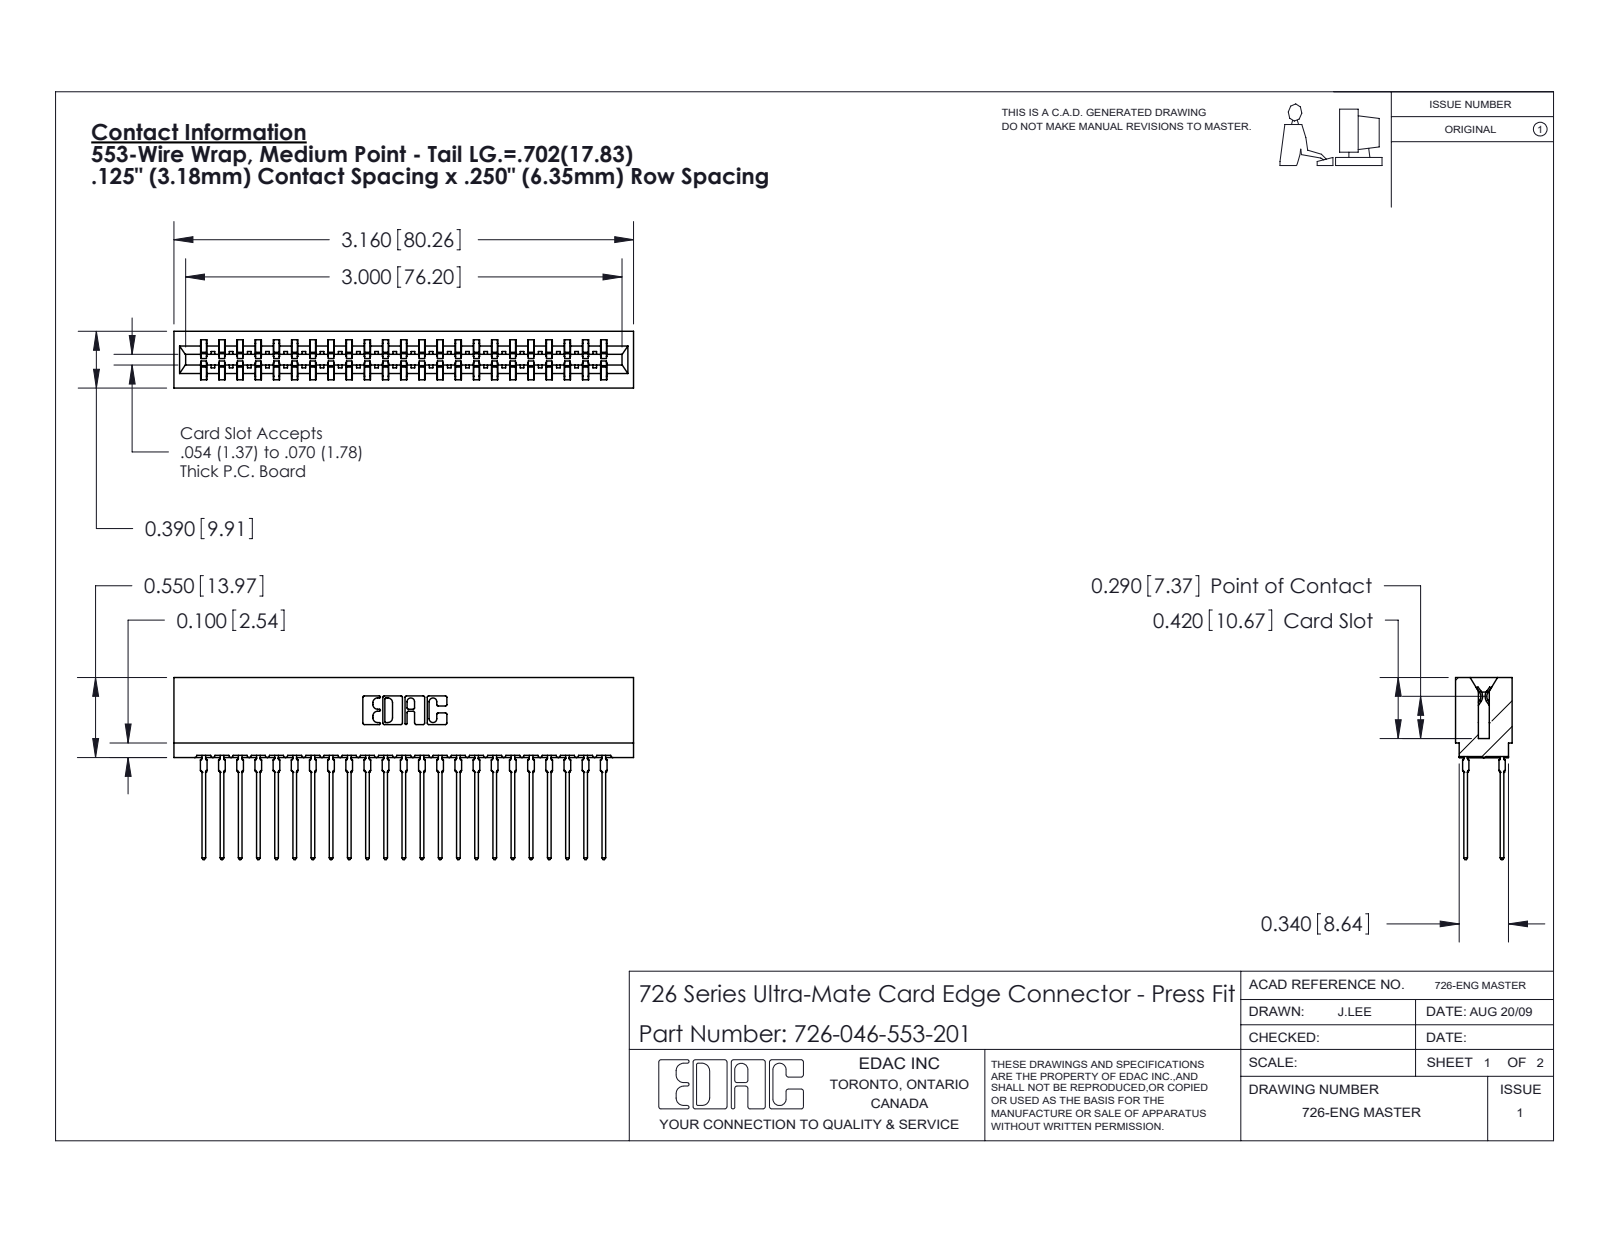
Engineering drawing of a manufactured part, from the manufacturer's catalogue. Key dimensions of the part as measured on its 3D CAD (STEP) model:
Part name (STEP PRODUCT): 726 Part_.515 Slot Depth - 01; 746-292-001_553; 726-046-553-201
STEP written by: SolidWorks 2020 (CONFIG_CONTROL_DESIGN)
Units: inches
Bodies: 47 solids, 4214 faces (2171 planar, 847 cylindrical, 1196 other)
Overall size (bounding box): 3.16 × 1.251 × 0.39
Volume: 0.469 in³ · Surface area: 20.79 in²
Partial cylindrical surfaces — rounded edges, fillets, slot ends (radius × count): R0.021 ×92, R0.015 ×24, R0.01 ×22, R0.005 ×8, R0.011 ×8, R0.007 ×6, R0.031 ×6, R0.026 ×3
Main face-to-face distances: 0.057, 0.333, 0.025, 0.307, 0.25, 0.083, 0.39, 0.275, 0.75, 0.042
